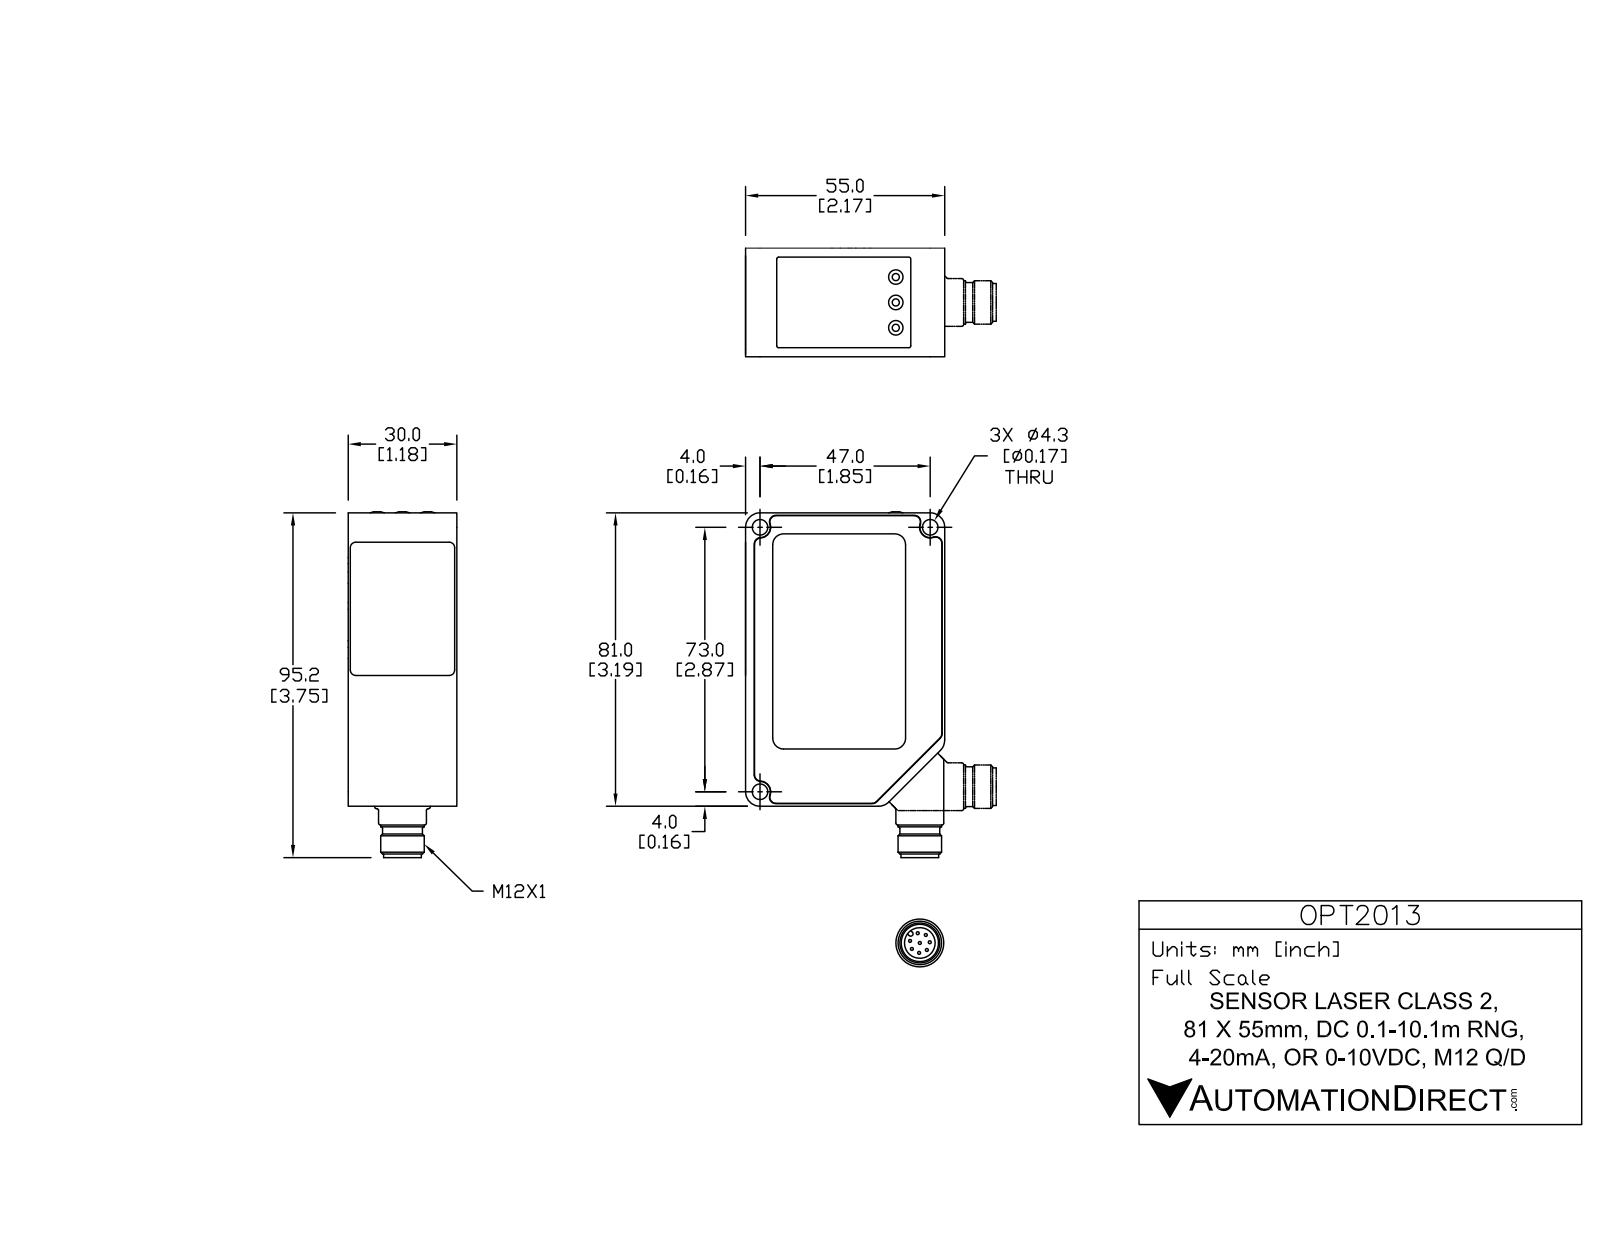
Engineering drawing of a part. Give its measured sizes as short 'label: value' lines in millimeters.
name: OPT2013
written by: SolidWorks 2013 (AUTOMOTIVE_DESIGN)
unit: mm
bodies: 21 solids, 321 faces (168 planar, 145 cylindrical, 8 other)
size: 95.83 × 55 × 30
volume: 122 812 mm³; area: 29 643 mm²
holes: 3× ⌀4.25, 1× ⌀5, 1× ⌀8.45
bosses: 8× ⌀0.82, 3× ⌀4.5, 1× ⌀18, 1× ⌀13.5, 1× ⌀12, 1× ⌀11, 1× ⌀10.3
rounds: 18× R2, 8× R1.25, 6× R2.1, 4× R0.5, 4× R1, 4× R1.5, 3× R1.9, 2× R0.75
face distances: 30, 55, 29.8, 3, 0.8, 81, 78, 54.8, 80.2, 2.2
hole spacings: 47, 73, 86.82
